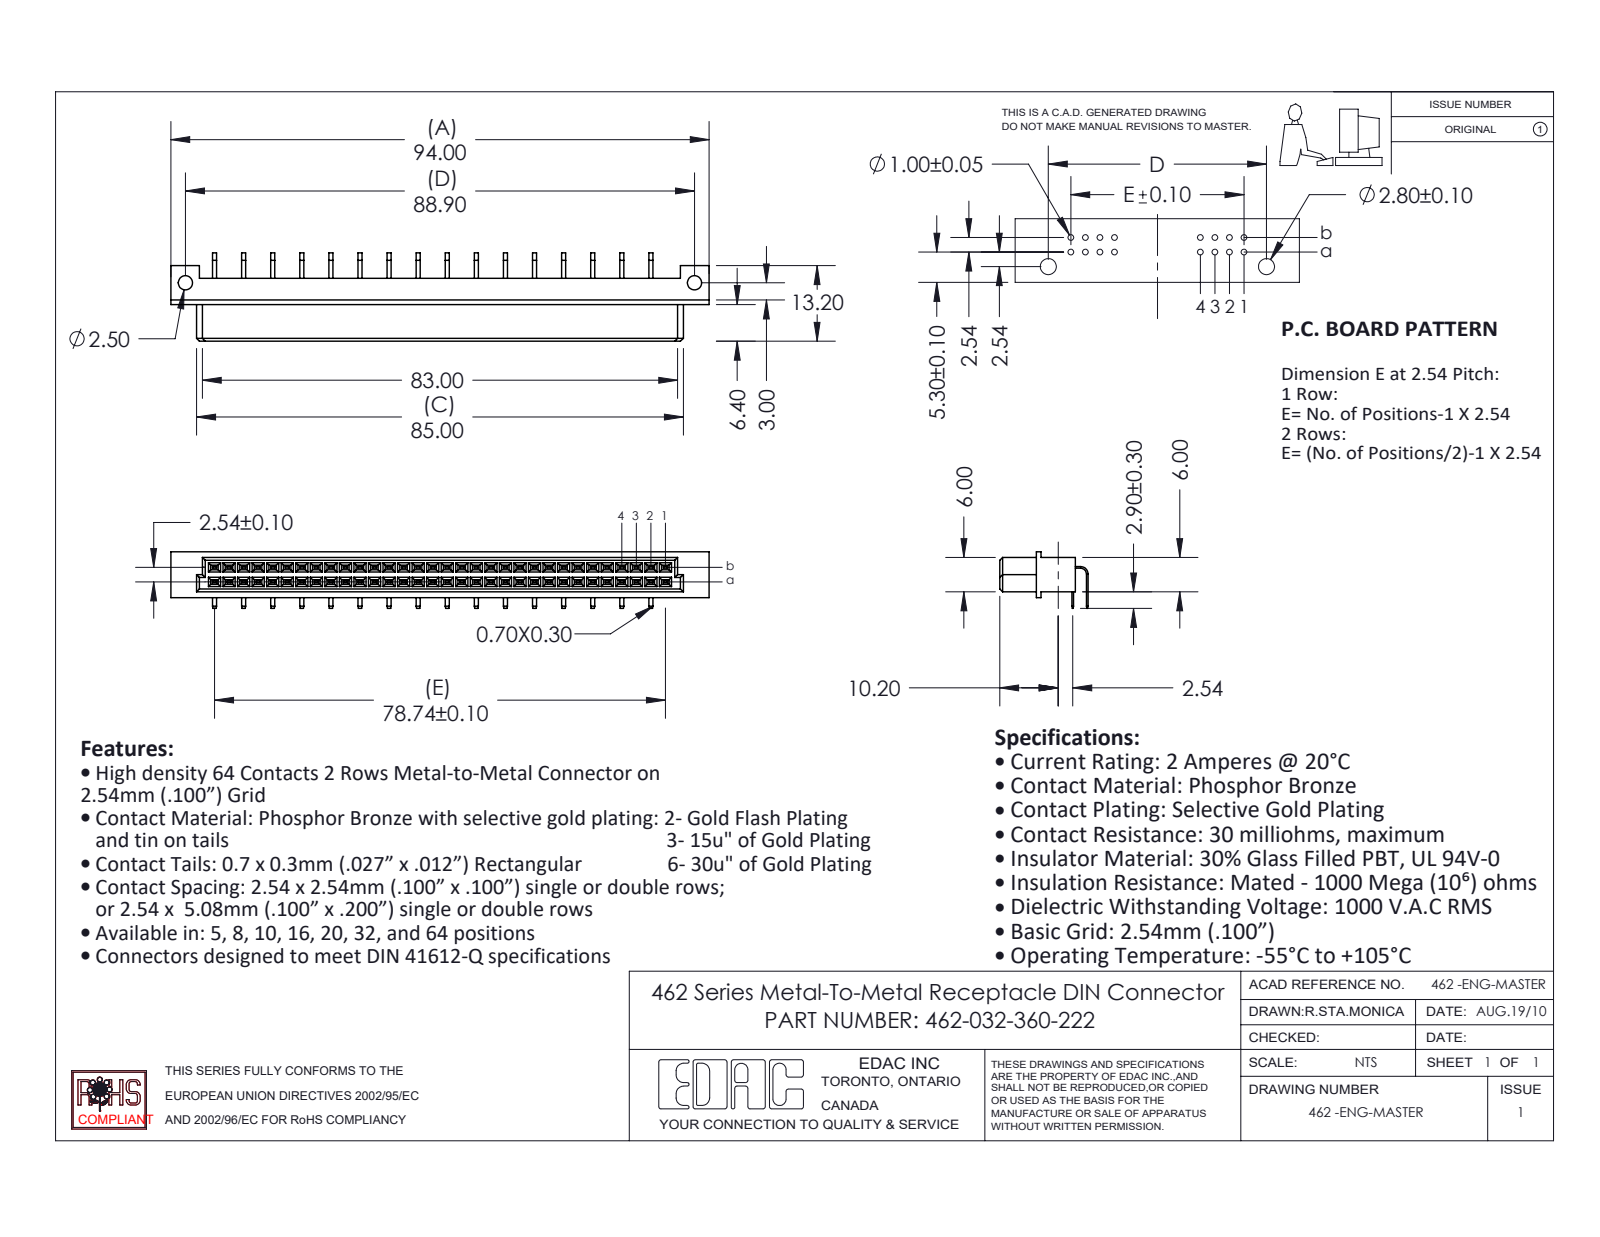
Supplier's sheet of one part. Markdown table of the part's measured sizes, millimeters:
| quantity | value |
| --- | --- |
| part name | 462-290-2; 462 Part_64; 462-290-1; 462-032-360-222 |
| STEP written by | SolidWorks 2020 (CONFIG_CONTROL_DESIGN) |
| units | millimeters |
| bodies | 33 solids, 1315 faces (1247 planar, 68 cylindrical, 0 other) |
| overall size | 94 × 15.43 × 9.9 |
| volume | 5 574 mm³ |
| surface area | 6 704 mm² |
| round holes (diameter × count) | 2.5 × 2 |
| partial cylindrical surfaces (radius × count) | 1.02 × 2, 1.32 × 2 |
| main face-to-face distances | 2.54, 6, 0.81, 0.55, 1.58, 1.88, 4.12, 4.42, 0.56, 4.6 |
| hole center spacings | 88.9 |
